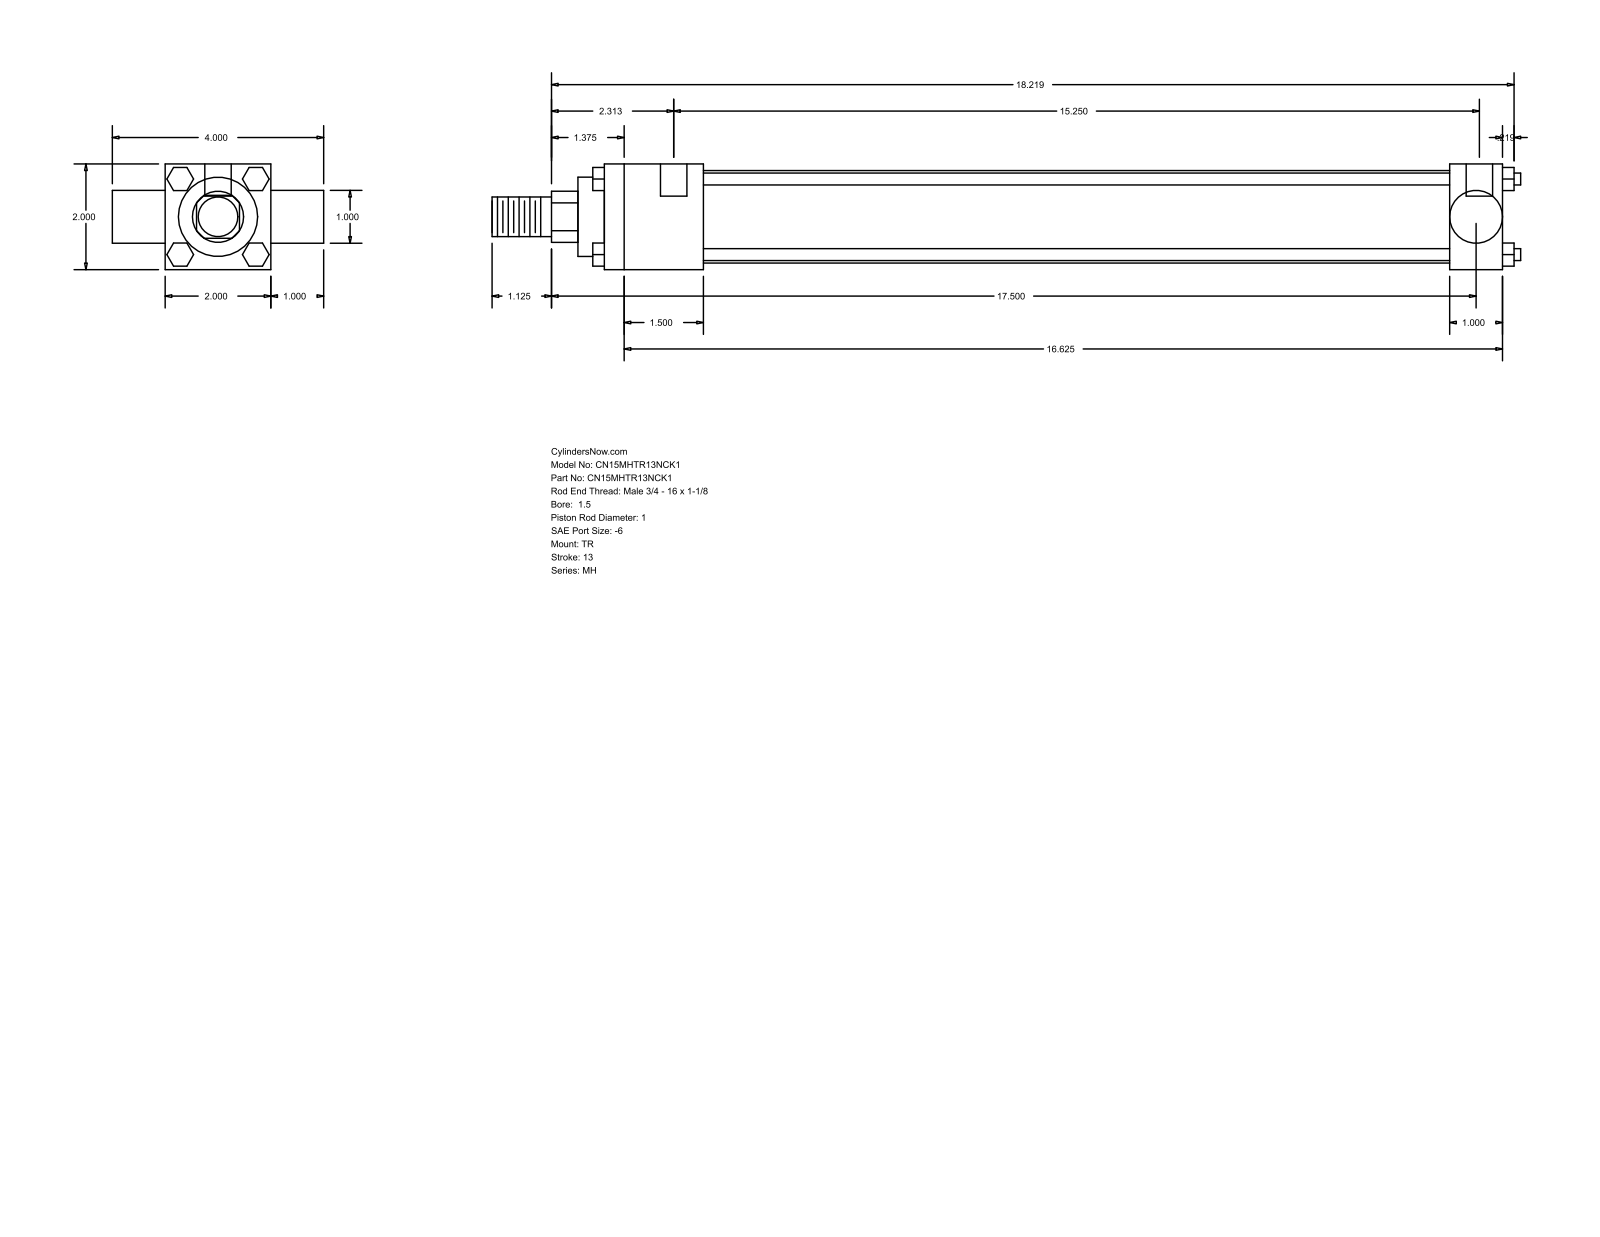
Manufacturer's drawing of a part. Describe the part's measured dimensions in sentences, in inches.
The part is named "MH_TR__0150_1". Its 3-D file was written by "GSSL Pune (CONFIG_CONTROL_DESIGN)". It is 0 solids with 120 faces: 92 planar, 28 cylindrical and 0 other. Overall it measures 19.469 by 4 by 2 inches. Round holes: 3 of diameter 0.219, 2 of diameter 0.5. Round bosses or shafts: 4 of diameter 0.225, 1 of diameter 1.75, 1 of diameter 1.5, 1 of diameter 1, 1 of diameter 0.998, 1 of diameter 0.75. Partial cylindrical surfaces (rounded edges, fillets, slot ends): 1 of radius 0.484. The main face-to-face distances are 2, 1, 17, 3, 1.875, 15.125, 16, 14.125, 4, 0.5. The hole center spacings are 0.125, 15.25, 15.375.
